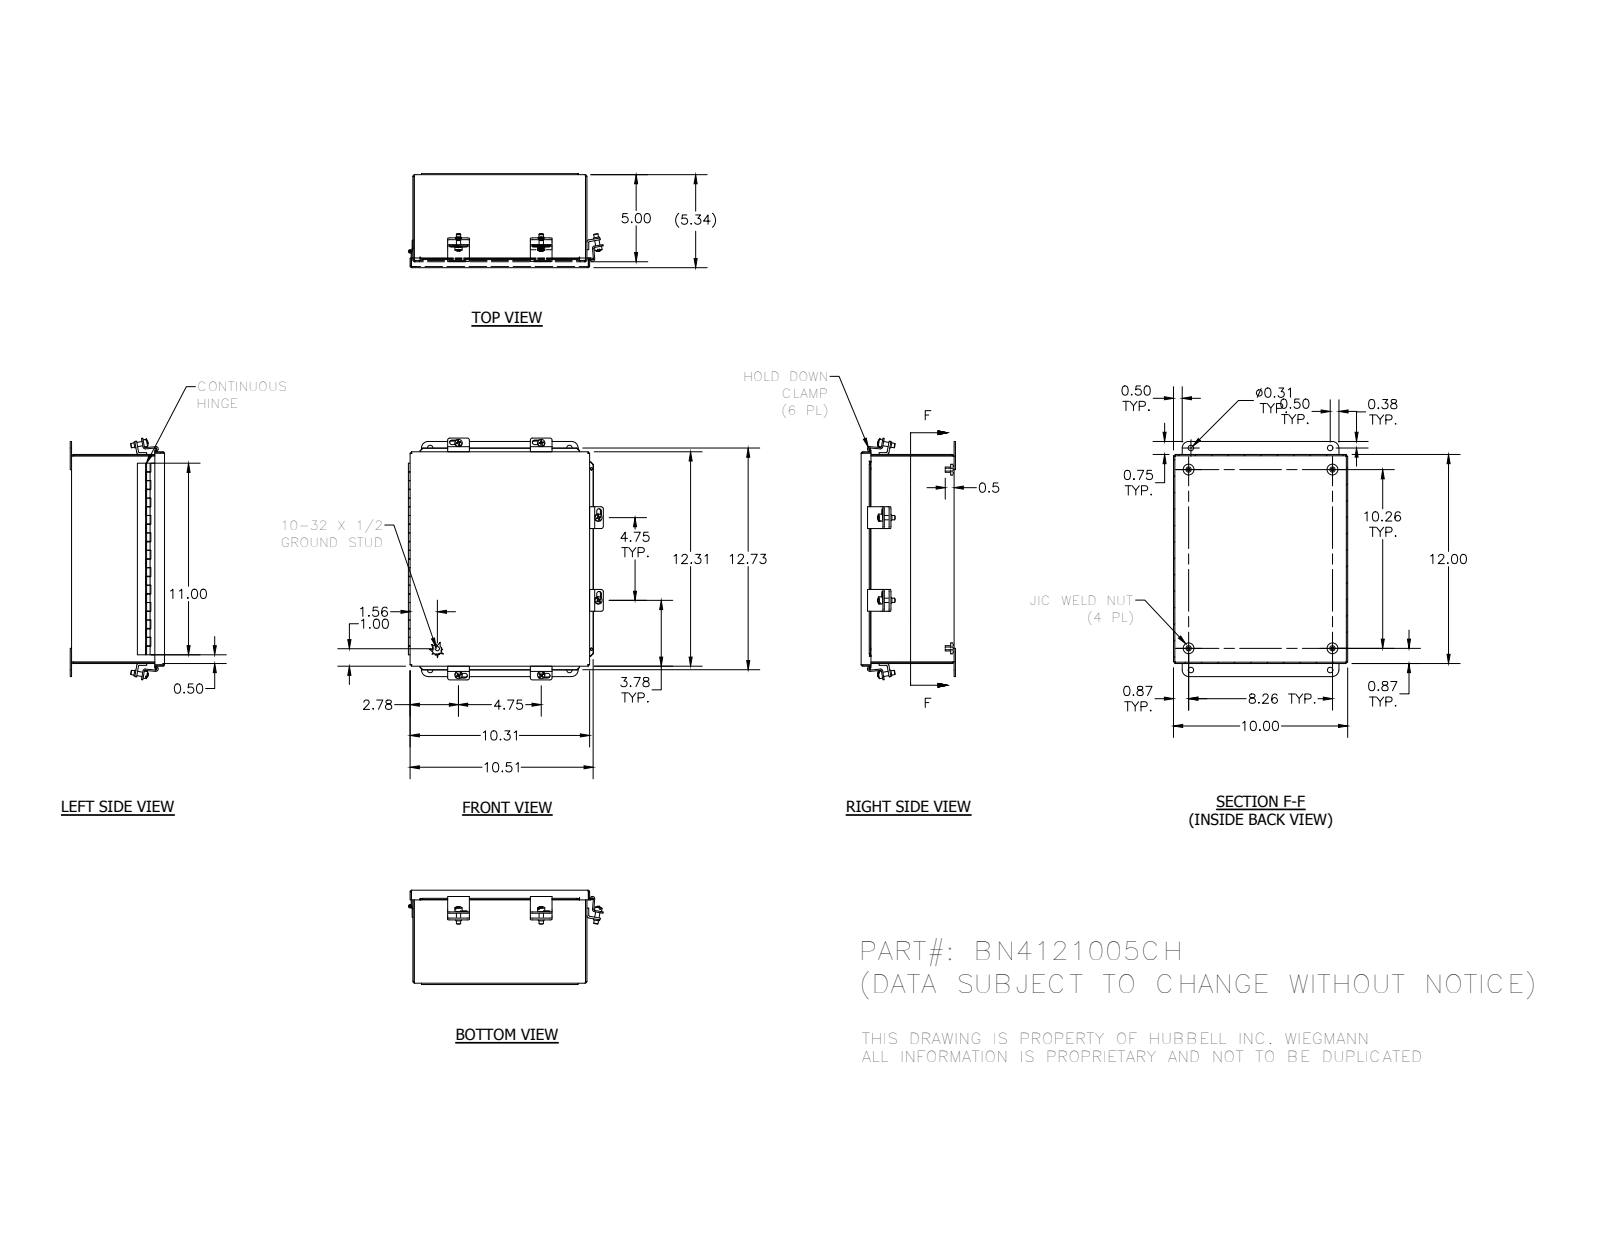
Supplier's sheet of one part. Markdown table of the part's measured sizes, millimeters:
| quantity | value |
| --- | --- |
| part name | B_1210CH_LID; 316166; 38811; 3499 (+8 more) |
| STEP written by | Autodesk Inventor 2016 (AUTOMOTIVE_DESIGN) |
| units | millimeters |
| bodies | 20 solids, 507 faces (325 planar, 131 cylindrical, 51 other) |
| overall size | 342.9 × 281.58 × 133.58 |
| volume | 712 710 mm³ |
| surface area | 776 897 mm² |
| round holes (diameter × count) | 3.96 × 4, 7.87 × 4, 3.56 × 2, 4.98 × 2, 2.96 × 1 |
| round bosses / shafts (diameter × count) | 15.88 × 4, 7.62 × 4, 6.35 × 3, 10.4 × 2, 8.74 × 2, 5.08 × 1, 4.83 × 1, 2.54 × 1 |
| partial cylindrical surfaces (radius × count) | 1.19 × 8, 3.07 × 8, 3.17 × 8, 1.98 × 4, 3.38 × 4, 3.48 × 4, 9.53 × 4, 0.79 × 3 |
| main face-to-face distances | 1.88, 130.18, 1.5, 131.68, 128.3, 129.8, 252.12, 302.92, 254, 250.24 |
| hole center spacings | 31.91, 292.12, 357.65, 203.2, 208.8, 208.81, 209.55, 260.35 |
